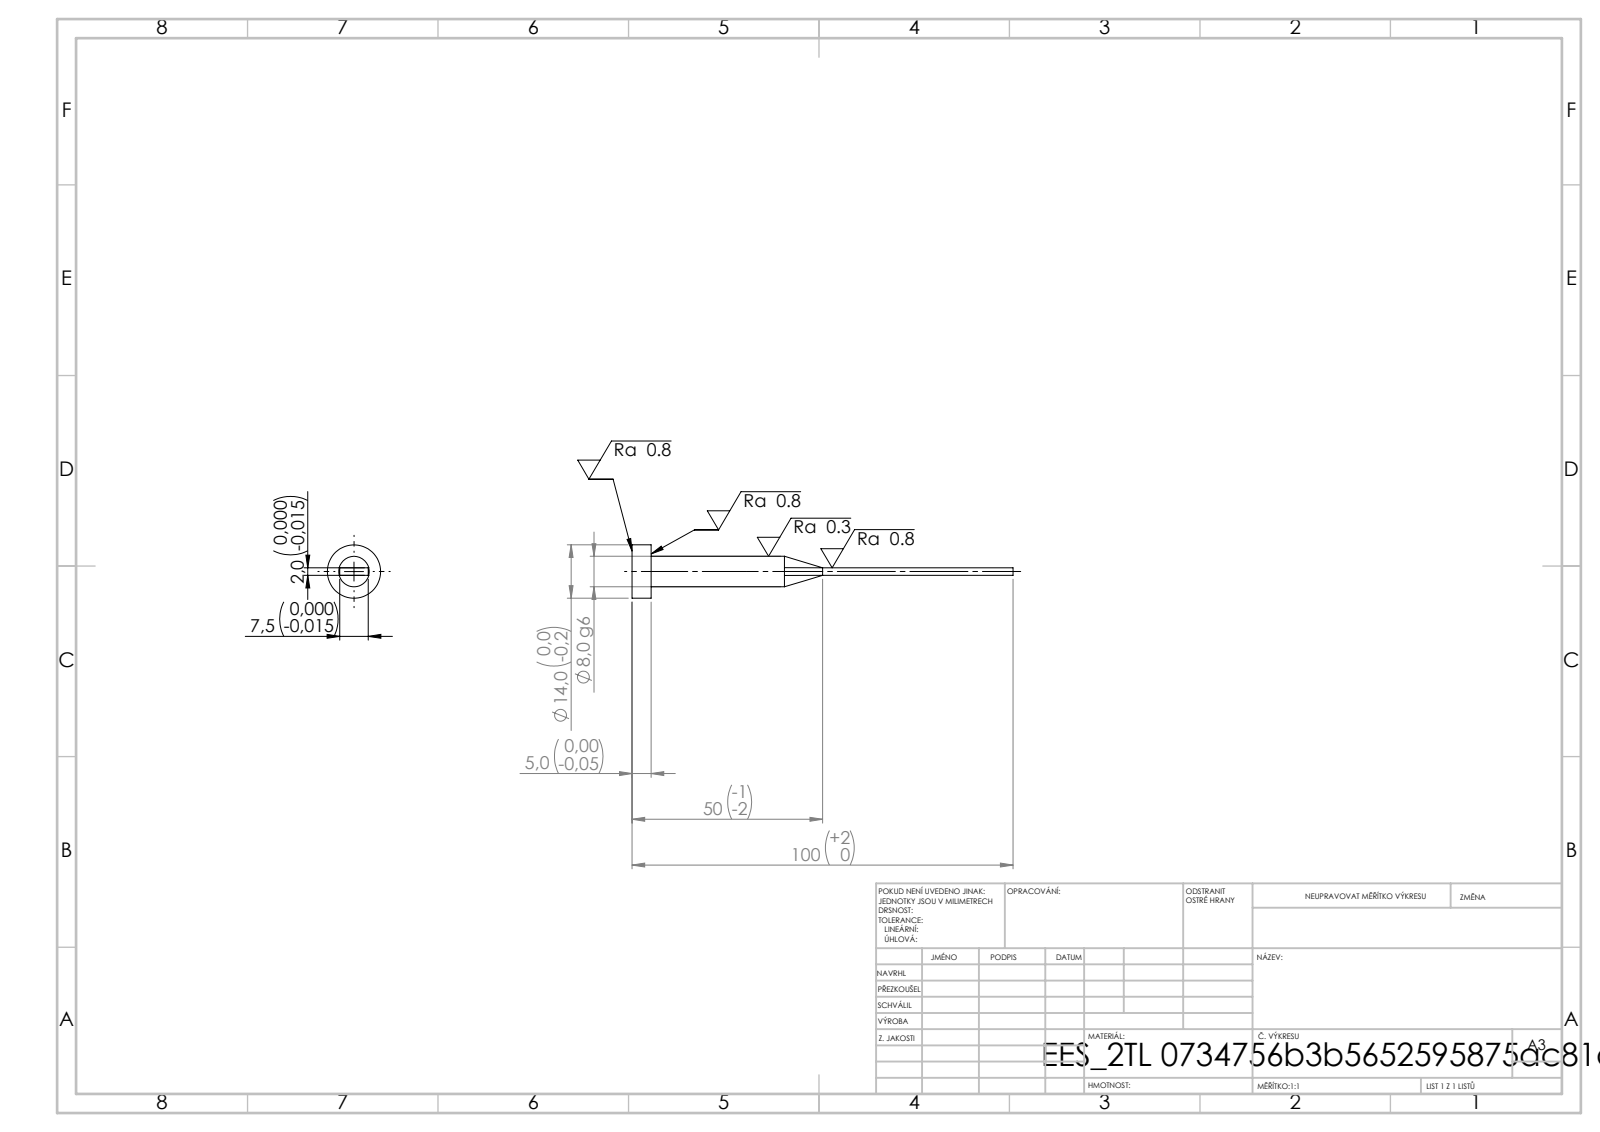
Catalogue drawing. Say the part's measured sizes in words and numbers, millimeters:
Its 3-D file was written by "SolidWorks 2019 (CONFIG_CONTROL_DESIGN)". It is 1 solid with 15 faces: 7 planar, 4 cylindrical and 4 other. Overall it measures 100 by 14 by 14 millimeters. Its volume is 3 593 cubic millimeters and its surface area 2 538 square millimeters. Round bosses or shafts: 1 of diameter 14, 1 of diameter 8. The main face-to-face distances are 2, 5, 7.5, 100, 95.
